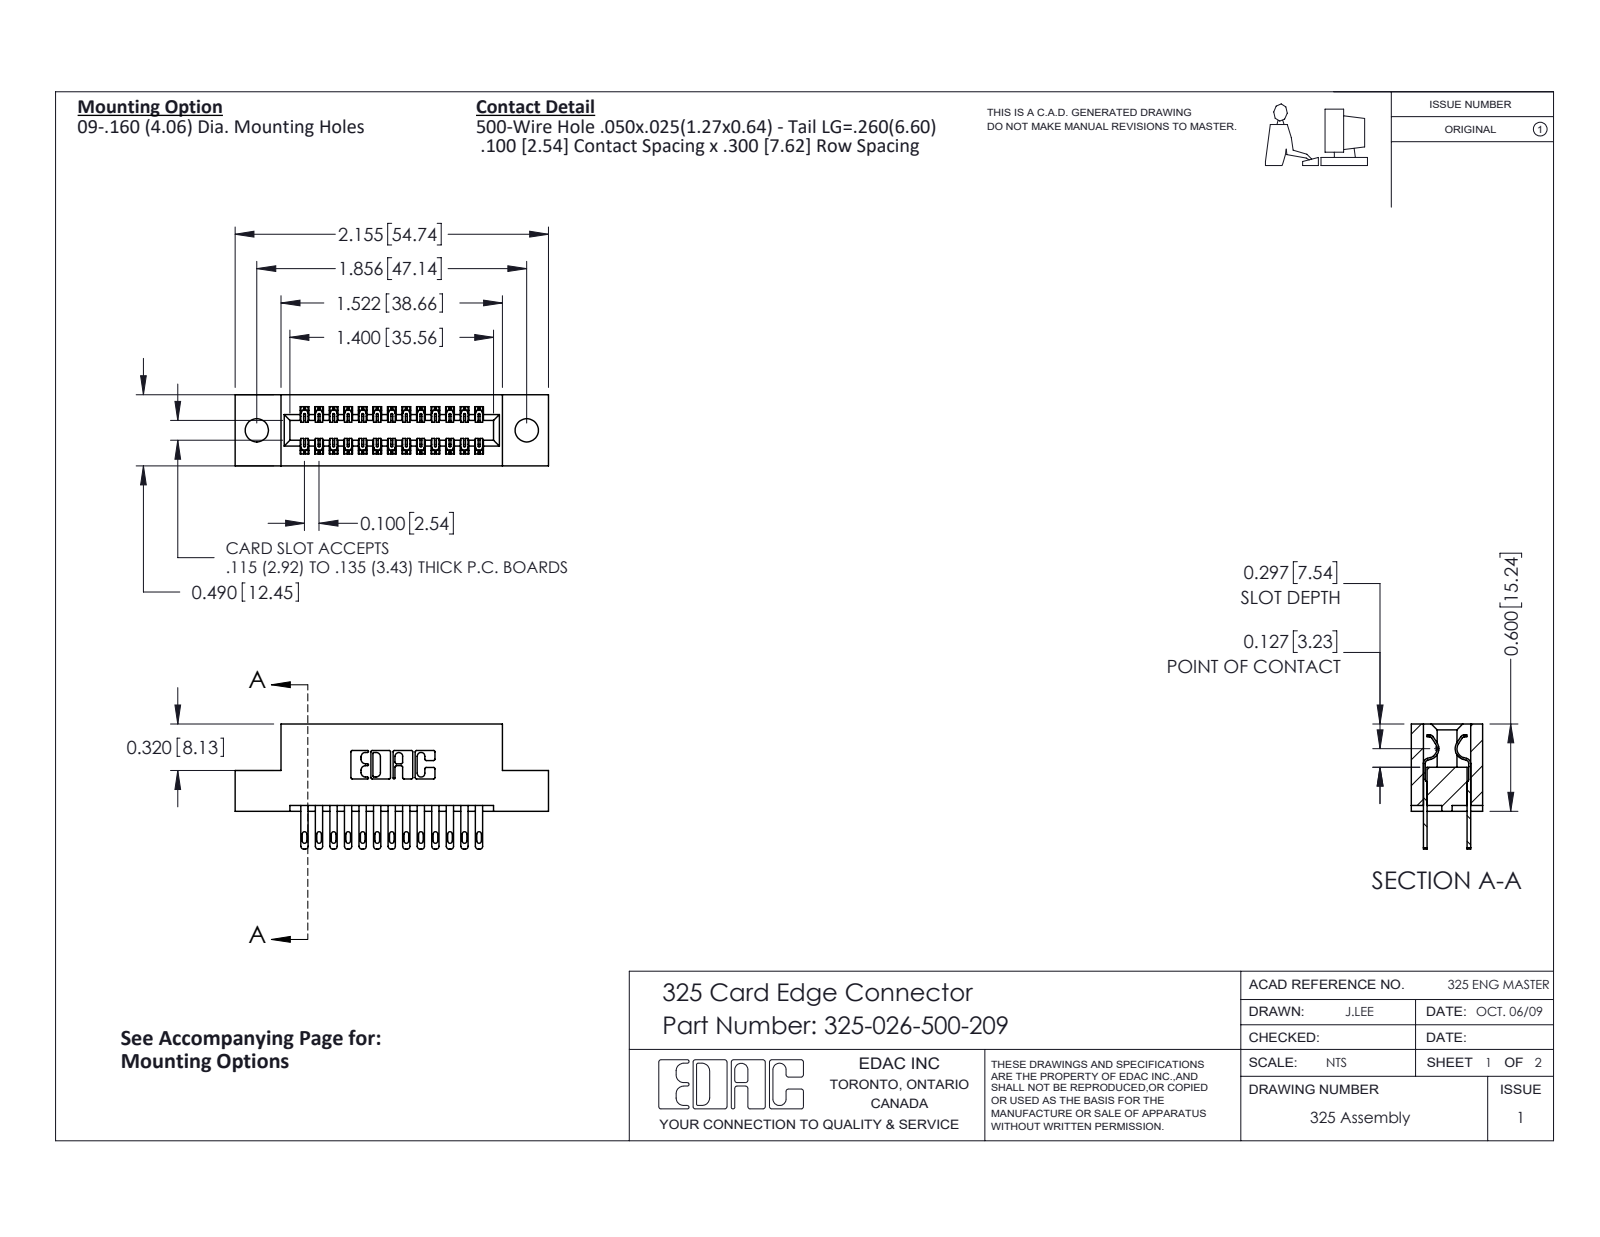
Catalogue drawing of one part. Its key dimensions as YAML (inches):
part_name: "325-292-001_325-293-100; 325 Part_.160 TH; 325-026-500-209"
step_written_by: "SolidWorks 2016 (CONFIG_CONTROL_DESIGN)"
units: inches
bodies: {solids: 27, faces: 1362, planar: 850, cylindrical: 512, other: 0}
overall_size: [2.155, 0.86, 0.49]
volume: 0.406
surface_area: 11.72
round_holes:
  - {diameter: 0.16, count: 2}
partial_cylinders:
  - {radius: 0.006, count: 39}
  - {radius: 0.016, count: 26}
  - {radius: 0.02, count: 26}
  - {radius: 0.01, count: 22}
  - {radius: 0.007, count: 6}
  - {radius: 0.031, count: 6}
  - {radius: 0.026, count: 3}
  - {radius: 0.014, count: 2}
face_to_face_distances: [0.083, 0.407, 0.3, 0.49, 0.107, 0.383, 0.025, 0.325, 0.04, 0.1]
hole_center_spacings: [1.856]
